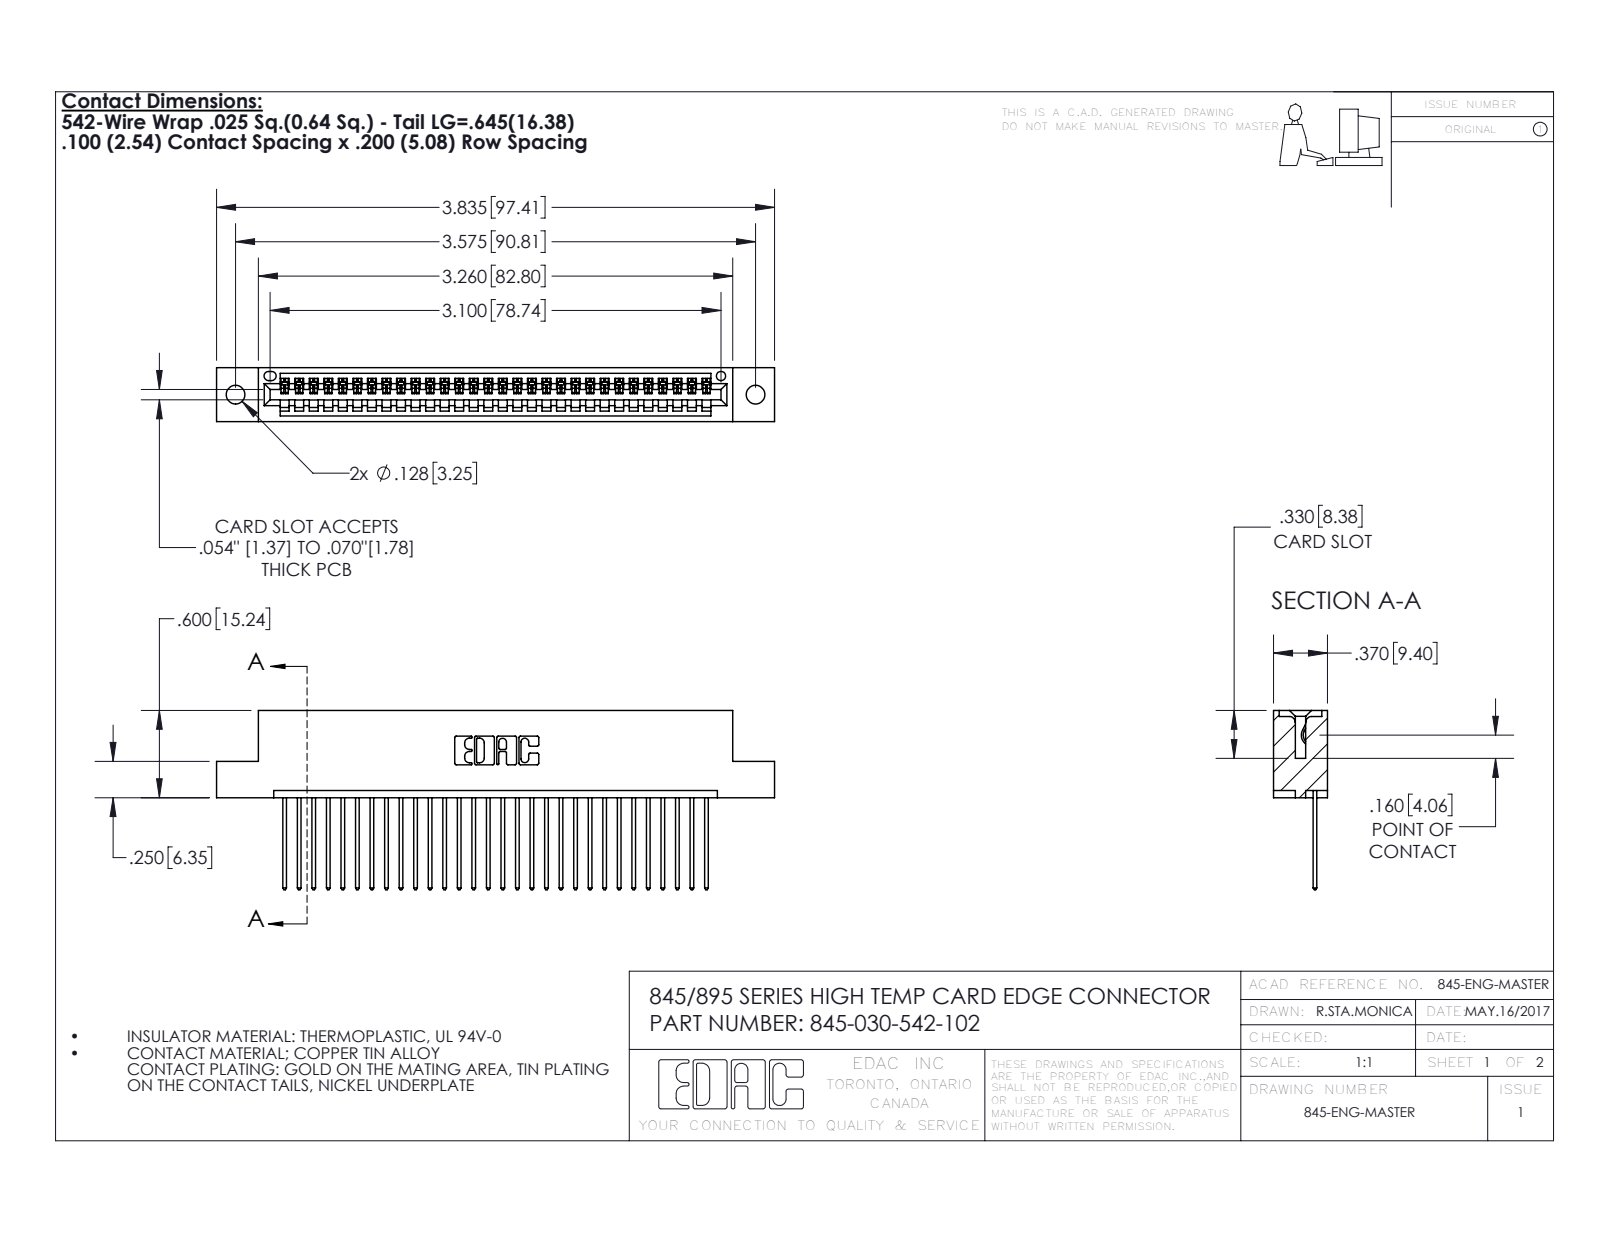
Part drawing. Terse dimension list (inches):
name: 345-292-001_345-293-142; 345 Part_Flush Mounting Lugs - 0.128 Dia; 345-030-542-102
written by: SolidWorks 2016 (CONFIG_CONTROL_DESIGN)
unit: in
bodies: 31 solids, 1866 faces (1280 planar, 586 cylindrical, 0 other)
size: 3.835 × 1.232 × 0.37
volume: 0.56 in³; area: 18.9 in²
holes: 2× ⌀0.128, 1× ⌀0.064
rounds: 60× R0.006, 60× R0.01, 22× R0.01, 6× R0.007, 6× R0.031, 3× R0.026, 2× R0.031, 2× R0.04
face distances: 0.298, 0.072, 0.2, 0.37, 0.098, 0.272, 0.025, 0.225, 0.149, 0.072
hole spacings: 0.27, 3.34, 3.575
